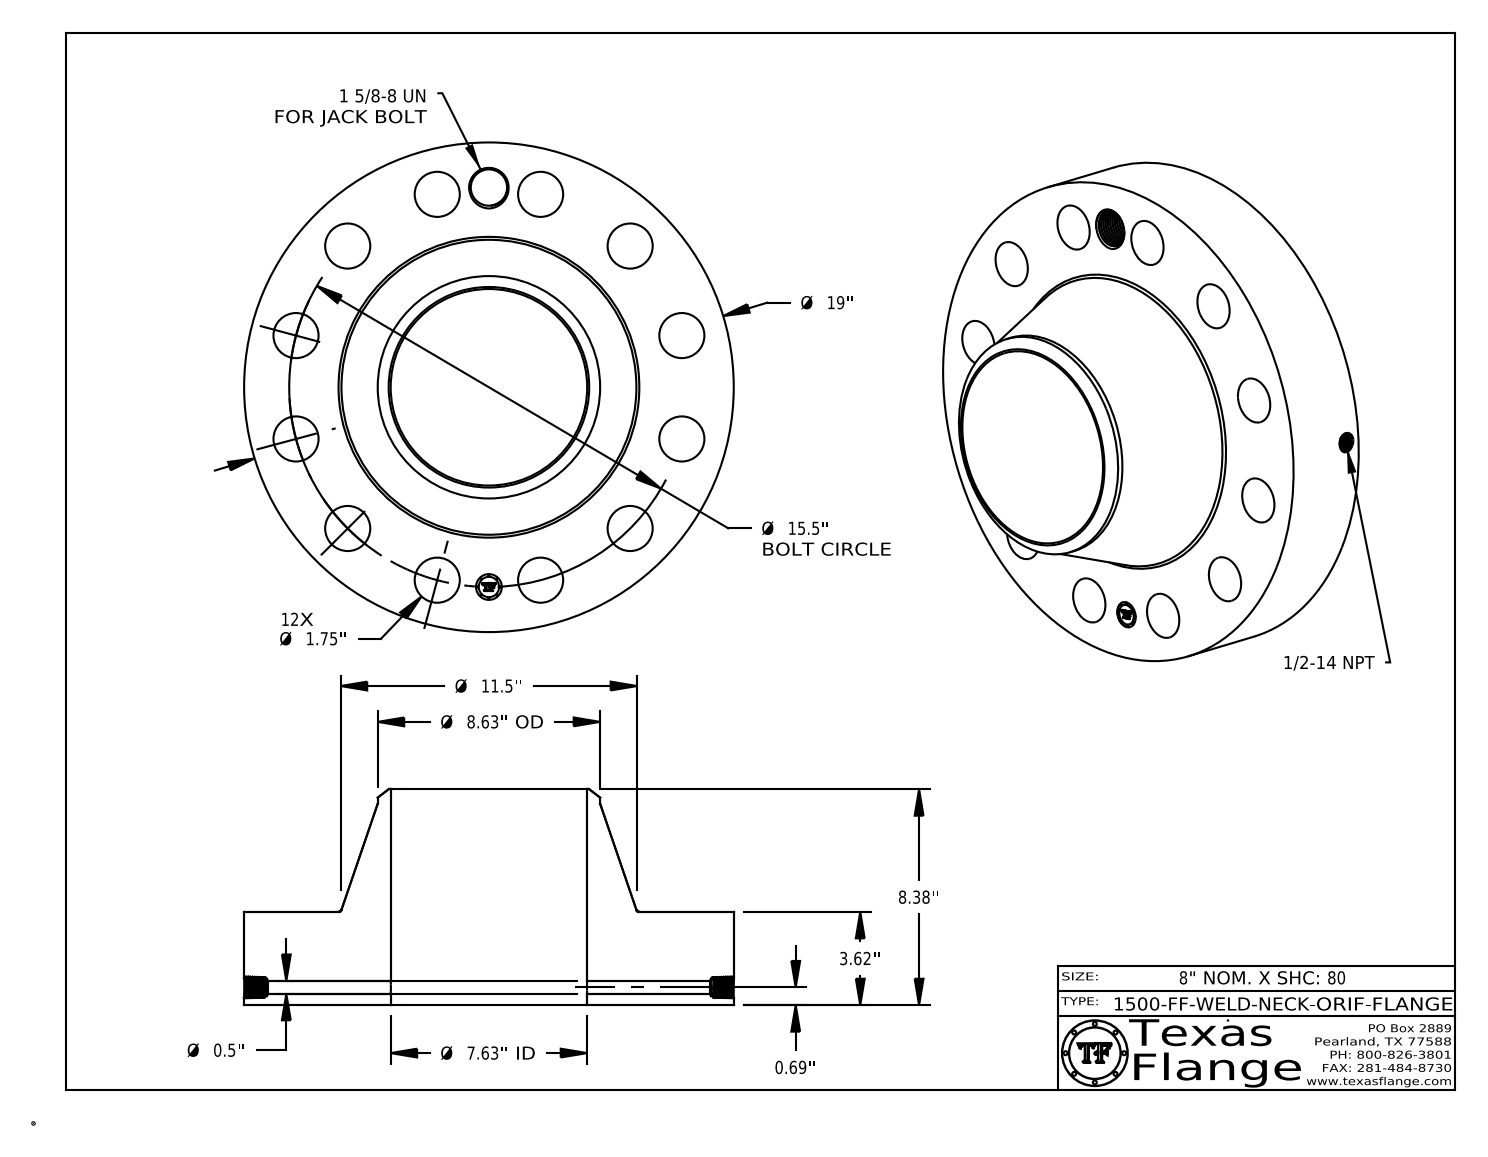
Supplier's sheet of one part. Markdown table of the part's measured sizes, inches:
| quantity | value |
| --- | --- |
| part name | 1500-FF-WELD-NECK |
| STEP written by | CATIA V5 STEP AP214 (AUTOMOTIVE_DESIGN) |
| units | inches |
| bodies | 1 solid, 858 faces (368 planar, 127 cylindrical, 363 other) |
| overall size | 19 × 19 × 8.38 |
| volume | 897.4 in³ |
| surface area | 1 229 in² |
| round holes (diameter × count) | 1.75 × 12, 0.5 × 1, 0.672 × 1, 1 × 1, 1.409 × 1, 7.625 × 1 |
| round bosses / shafts (diameter × count) | 0.061 × 8, 19 × 1, 8.63 × 1, 0.788 × 1 |
| main face-to-face distances | 3.62, 8.38, 4.76, 3.605, 0.015, 4.775, 0.298, 0.293, 0.054, 0.248 |
| hole center spacings | 7.75, 13.423, 14.972, 4.011, 7.75, 10.96, 15.5, 2.023 |
